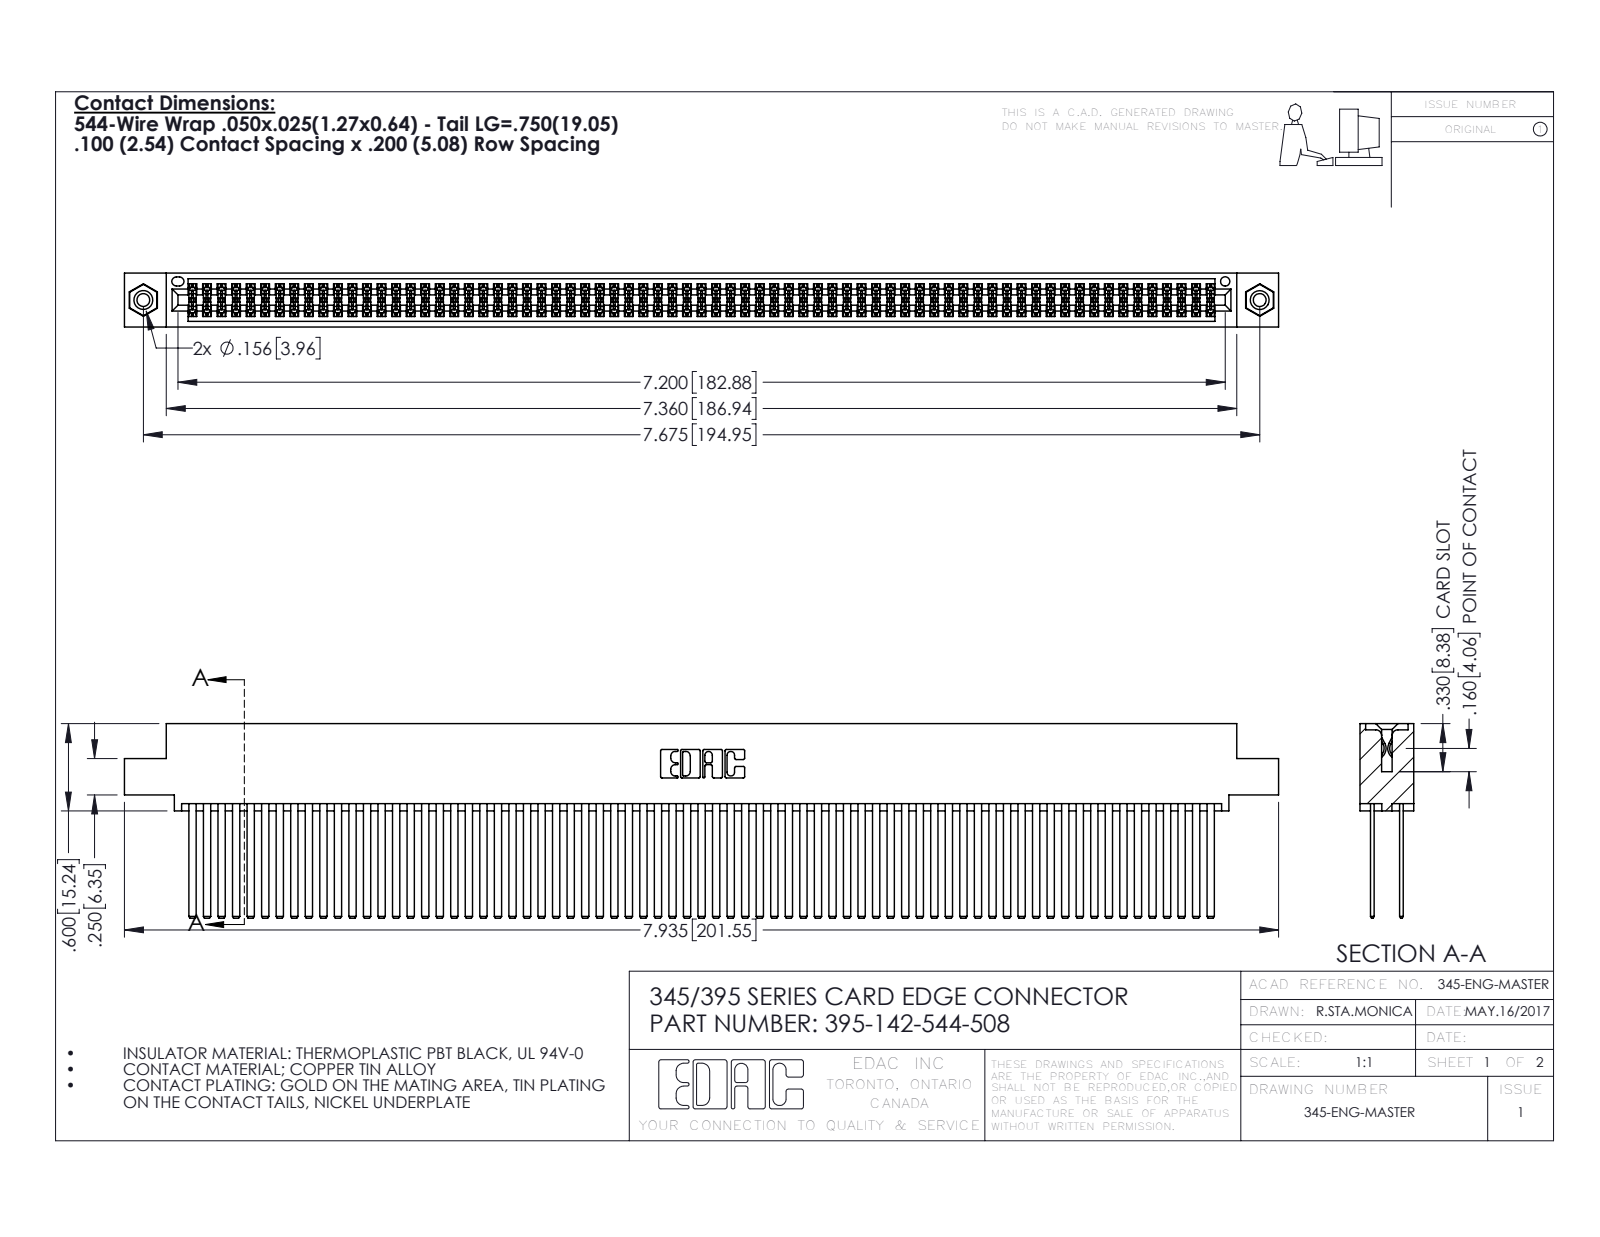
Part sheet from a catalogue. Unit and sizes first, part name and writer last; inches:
Units: inches
Overall size (bounding box): 7.935 × 1.337 × 0.37
Round holes (diameter × count): ⌀0.089 ×2, ⌀0.125 ×2, ⌀0.156 ×2, ⌀0.064 ×1
Round bosses / shafts (diameter × count): ⌀0.155 ×2
Partial cylindrical surfaces — rounded edges, fillets, slot ends (radius × count): R0.006 ×213, R0.01 ×22, R0.007 ×6, R0.031 ×6, R0.026 ×3, R0.014 ×2, R0.019 ×2, R0.022 ×2
Main face-to-face distances: 0.2, 0.025, 0.072, 0.098, 0.272, 0.298, 0.225, 0.175, 0.37, 0.149
Hole centre spacings: 0.27, 7.439, 7.675
Volume: 1.328 in³ · Surface area: 59.93 in²
Bodies: 145 solids, 6438 faces (4234 planar, 2188 cylindrical, 16 other)
Part name (STEP PRODUCT): 395-142-544-508; 345-250-001_345-250-003-102; 345-292-001_345-293-144; 345 Part_0.110 Offset - 0.156 Dia-TI
STEP written by: SolidWorks 2016 (CONFIG_CONTROL_DESIGN)
